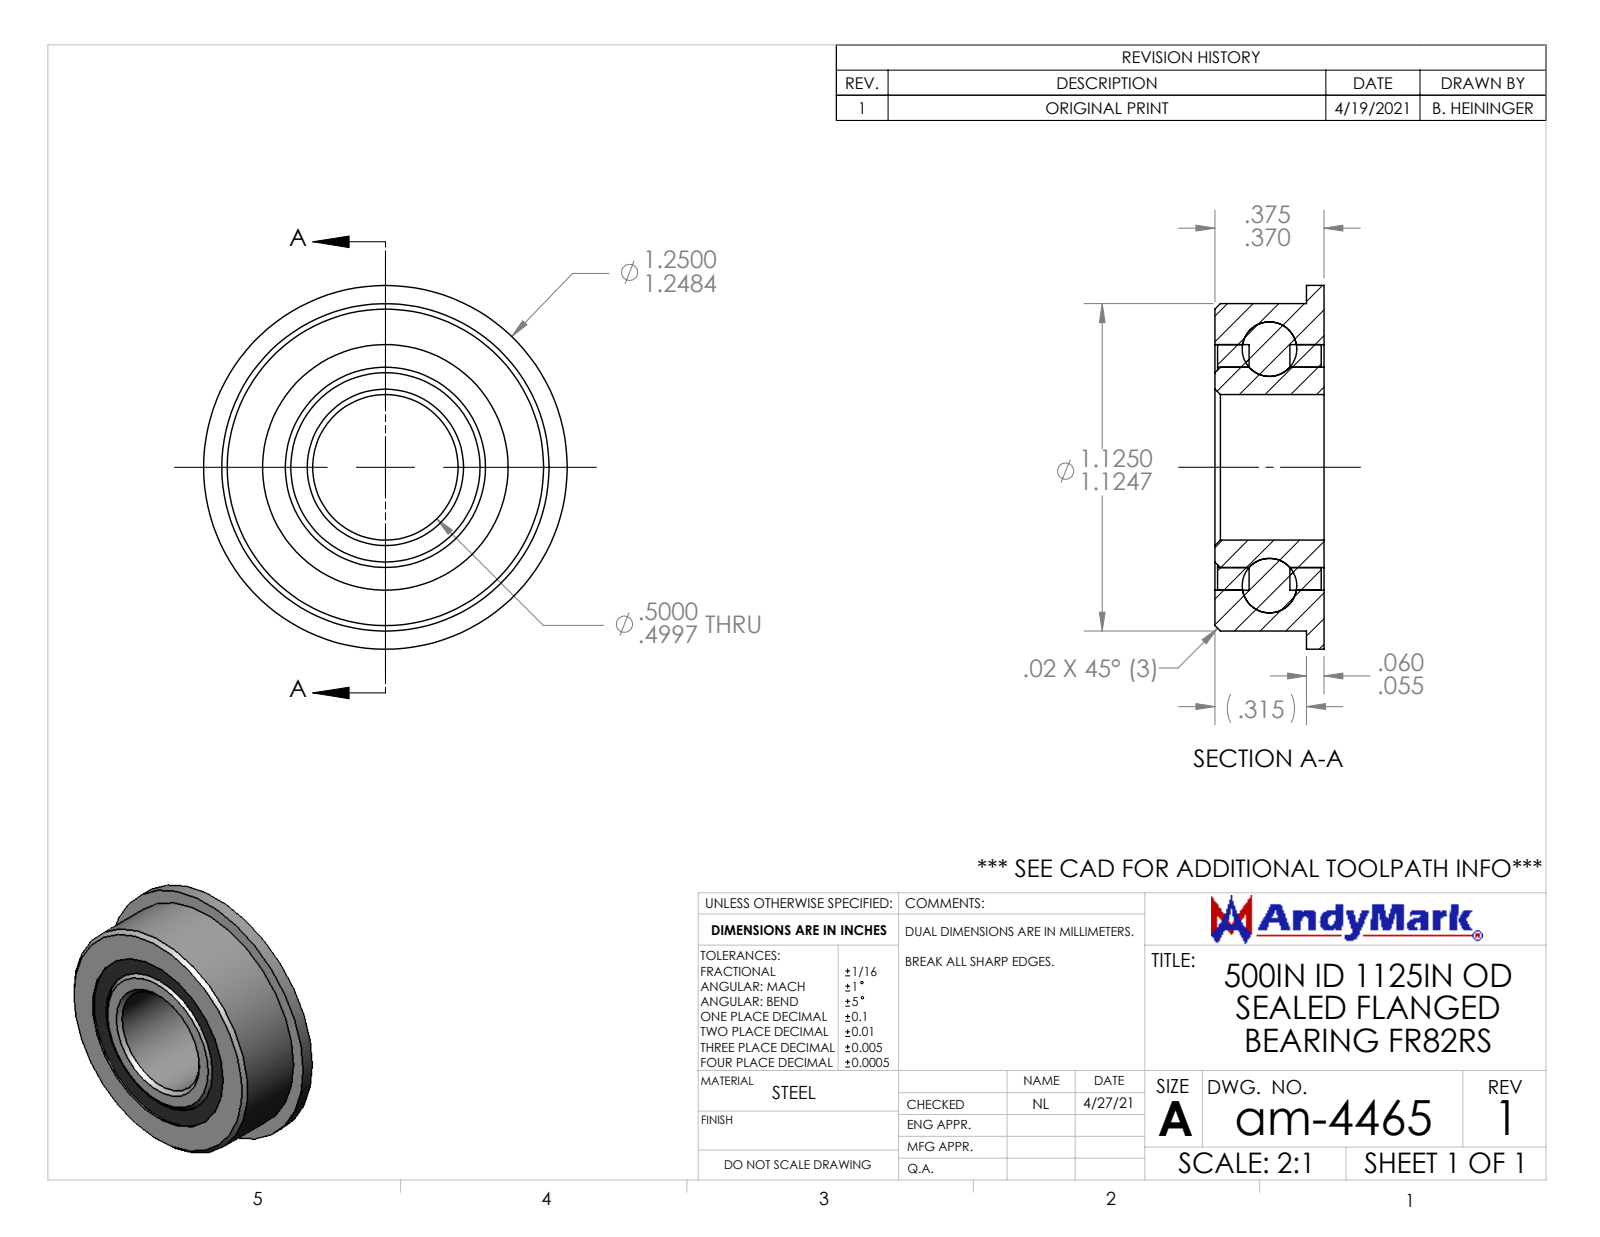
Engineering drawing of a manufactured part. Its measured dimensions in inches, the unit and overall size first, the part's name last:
Units: inches
Overall size (bounding box): 1.25 × 1.25 × 0.375
Round holes (diameter × count): ⌀0.5 ×1, ⌀0.688 ×1, ⌀0.844 ×1
Round bosses / shafts (diameter × count): ⌀1.25 ×1, ⌀1.125 ×1
Main face-to-face distances: 0.375, 0.365, 0.117, 0.257, 0.108, 0.248, 0.06, 0.315, 0.05, 0.057
Volume: 0.286 in³ · Surface area: 8.773 in²
Bodies: 16 solids, 67 faces (9 planar, 22 cylindrical, 36 other)
Part name (STEP PRODUCT): am-4465 1-2 in ID 1 1-8 in OD Sealed Flanged Bearing FR82RS
STEP written by: SolidWorks 2019 (AUTOMOTIVE_DESIGN)
